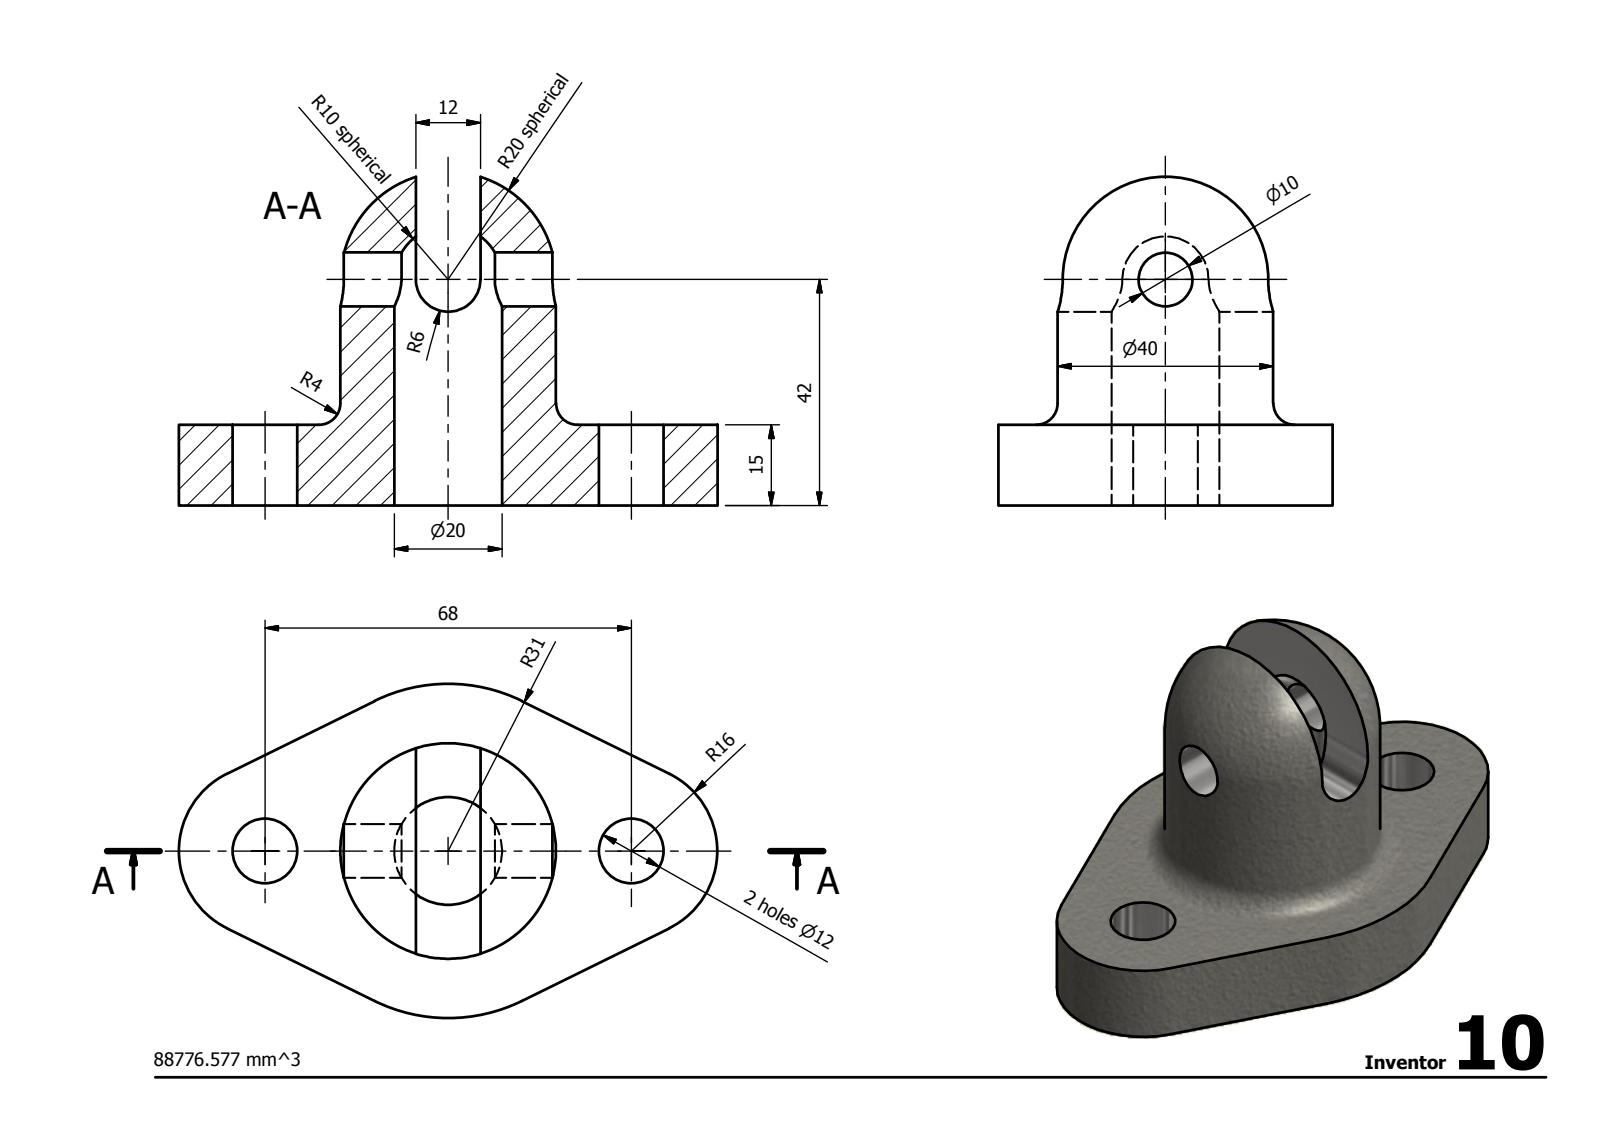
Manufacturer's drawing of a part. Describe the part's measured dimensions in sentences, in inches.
Its 3-D file was written by "Autodesk Inventor 2014 (AUTOMOTIVE_DESIGN)". It is 1 solid with 25 faces: 8 planar, 12 cylindrical and 5 other. Overall it measures 3.937 by 2.441 by 2.405 inches. Its volume is 5.418 cubic inches and its surface area 32.19 square inches. Round holes: 2 of diameter 0.472, 1 of diameter 0.394, 1 of diameter 0.787. Round bosses or shafts: 1 of diameter 1.575. Partial cylindrical surfaces (rounded edges, fillets, slot ends): 2 of radius 0.63, 1 of radius 0.236, 1 of radius 1.22. The main face-to-face distances are 0.591, 2.44, 0.472. The hole center spacings are 1.339, 2.677.
